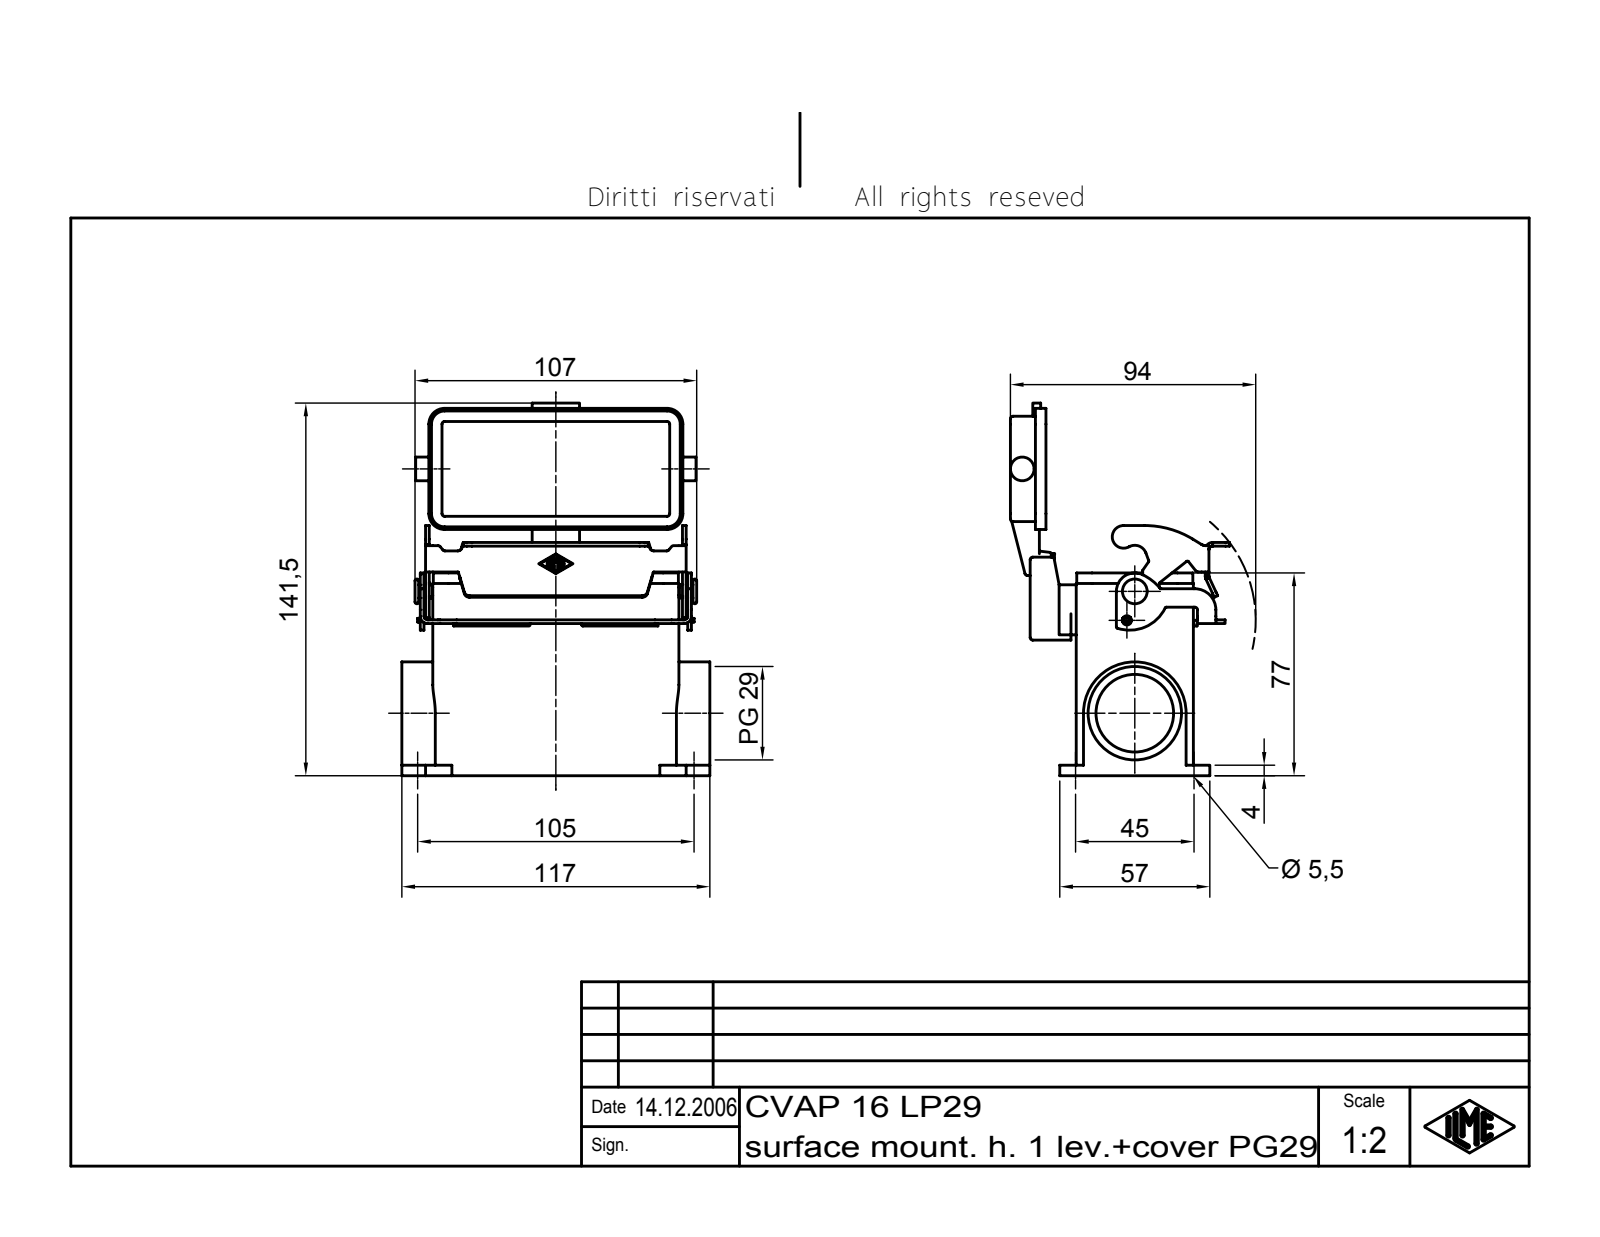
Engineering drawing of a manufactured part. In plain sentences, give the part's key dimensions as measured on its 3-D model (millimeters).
The part is named "CVAP 16 LP29". Its 3-D file was written by "Autodesk Inventor 7 (AUTOMOTIVE_DESIGN)". It is 4 solids with 590 faces: 232 planar, 193 cylindrical and 165 other. Overall it measures 141.5 by 117 by 83.23 millimeters. Its volume is 149 545 cubic millimeters and its surface area 87 671 square millimeters. Round holes: 4 of diameter 5.5, 1 of diameter 3.5, 1 of diameter 4, 1 of diameter 29.48, 1 of diameter 35.48. Round bosses or shafts: 2 of diameter 5, 1 of diameter 9, 1 of diameter 7, 1 of diameter 3.2, 1 of diameter 3. Partial cylindrical surfaces (rounded edges, fillets, slot ends): 32 of radius 1, 15 of radius 0.25, 10 of radius 0.5, 9 of radius 1.5, 8 of radius 6, 7 of radius 2, 6 of radius 1.4, 6 of radius 2.8. The main face-to-face distances are 4, 40.5, 44.5, 36.5, 2, 69.5, 65.5, 29, 25, 11.5. The hole center spacings are 45, 105, 114.24, 35.39.
